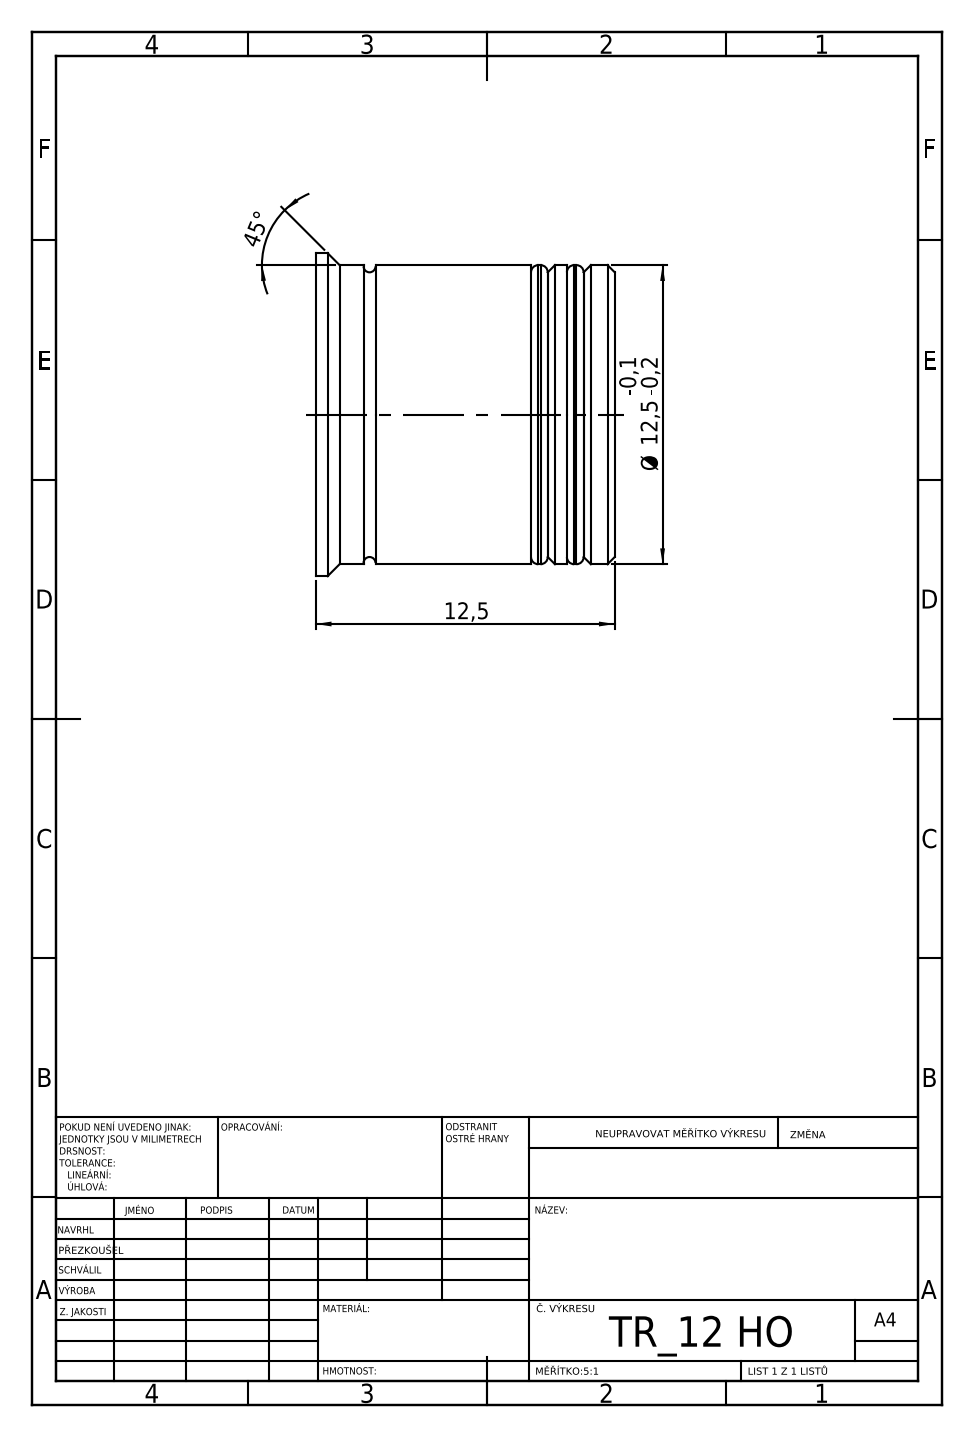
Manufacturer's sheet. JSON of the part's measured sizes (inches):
{"step_written_by": "SolidWorks 2019 (CONFIG_CONTROL_DESIGN)", "units": "inches", "bodies": {"solids": 3, "faces": 74, "planar": 29, "cylindrical": 25, "other": 20}, "overall_size": [0.531, 0.531, 0.492], "volume_in3": 0.098, "surface_area_in2": 2.198, "round_bosses_or_shafts": [[0.531, 1], [0.492, 1], [0.469, 1], [0.374, 1]], "face_to_face_distances": [0.059, 0.028, 0.079, 0.374, 0.138, 0.051, 0.11, 0.087, 0.031, 0.343]}
